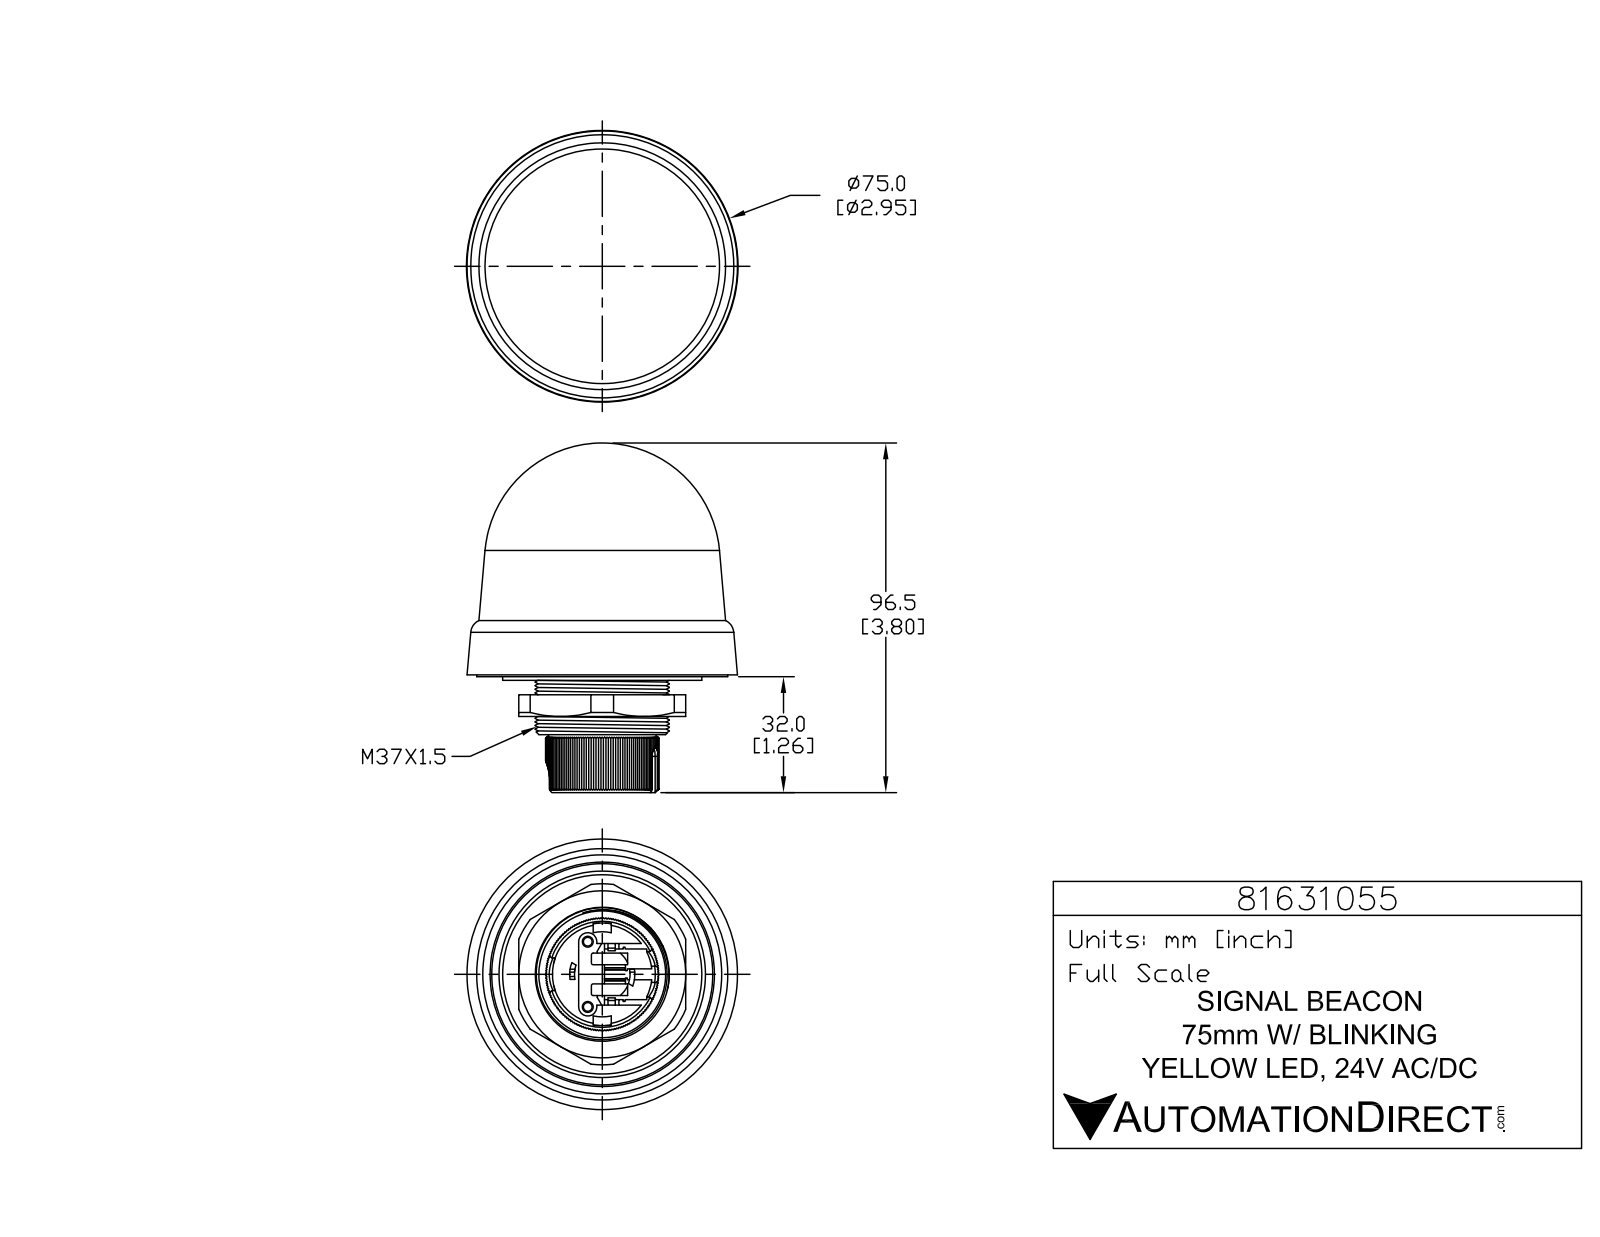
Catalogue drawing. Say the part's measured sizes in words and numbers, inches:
The part is named "81631055". Its 3-D file was written by "SolidWorks 2019 (CONFIG_CONTROL_DESIGN)". It is 3 solids with 560 faces: 432 planar, 80 cylindrical and 48 other. Overall it measures 3.799 by 2.941 by 2.941 inches. Its volume is 12.36 cubic inches and its surface area 58.68 square inches. Round holes: 2 of diameter 0.094, 2 of diameter 0.118, 1 of diameter 0.604, 1 of diameter 1.142. Round bosses or shafts: 2 of diameter 0.217, 2 of diameter 0.067, 1 of diameter 2.165, 1 of diameter 1.457, 1 of diameter 0.925. Partial cylindrical surfaces (rounded edges, fillets, slot ends): 6 of radius 0.008, 6 of radius 0.039, 4 of radius 0.02, 2 of radius 0.031, 2 of radius 0.079, 2 of radius 0.098, 1 of radius 0.177, 1 of radius 0.354. The main face-to-face distances are 0.177, 0.354, 0.197, 0.433, 0.512, 0.335, 0.059, 0.394, 0.118, 0.157. The hole center spacings are 0.388, 0.709.
